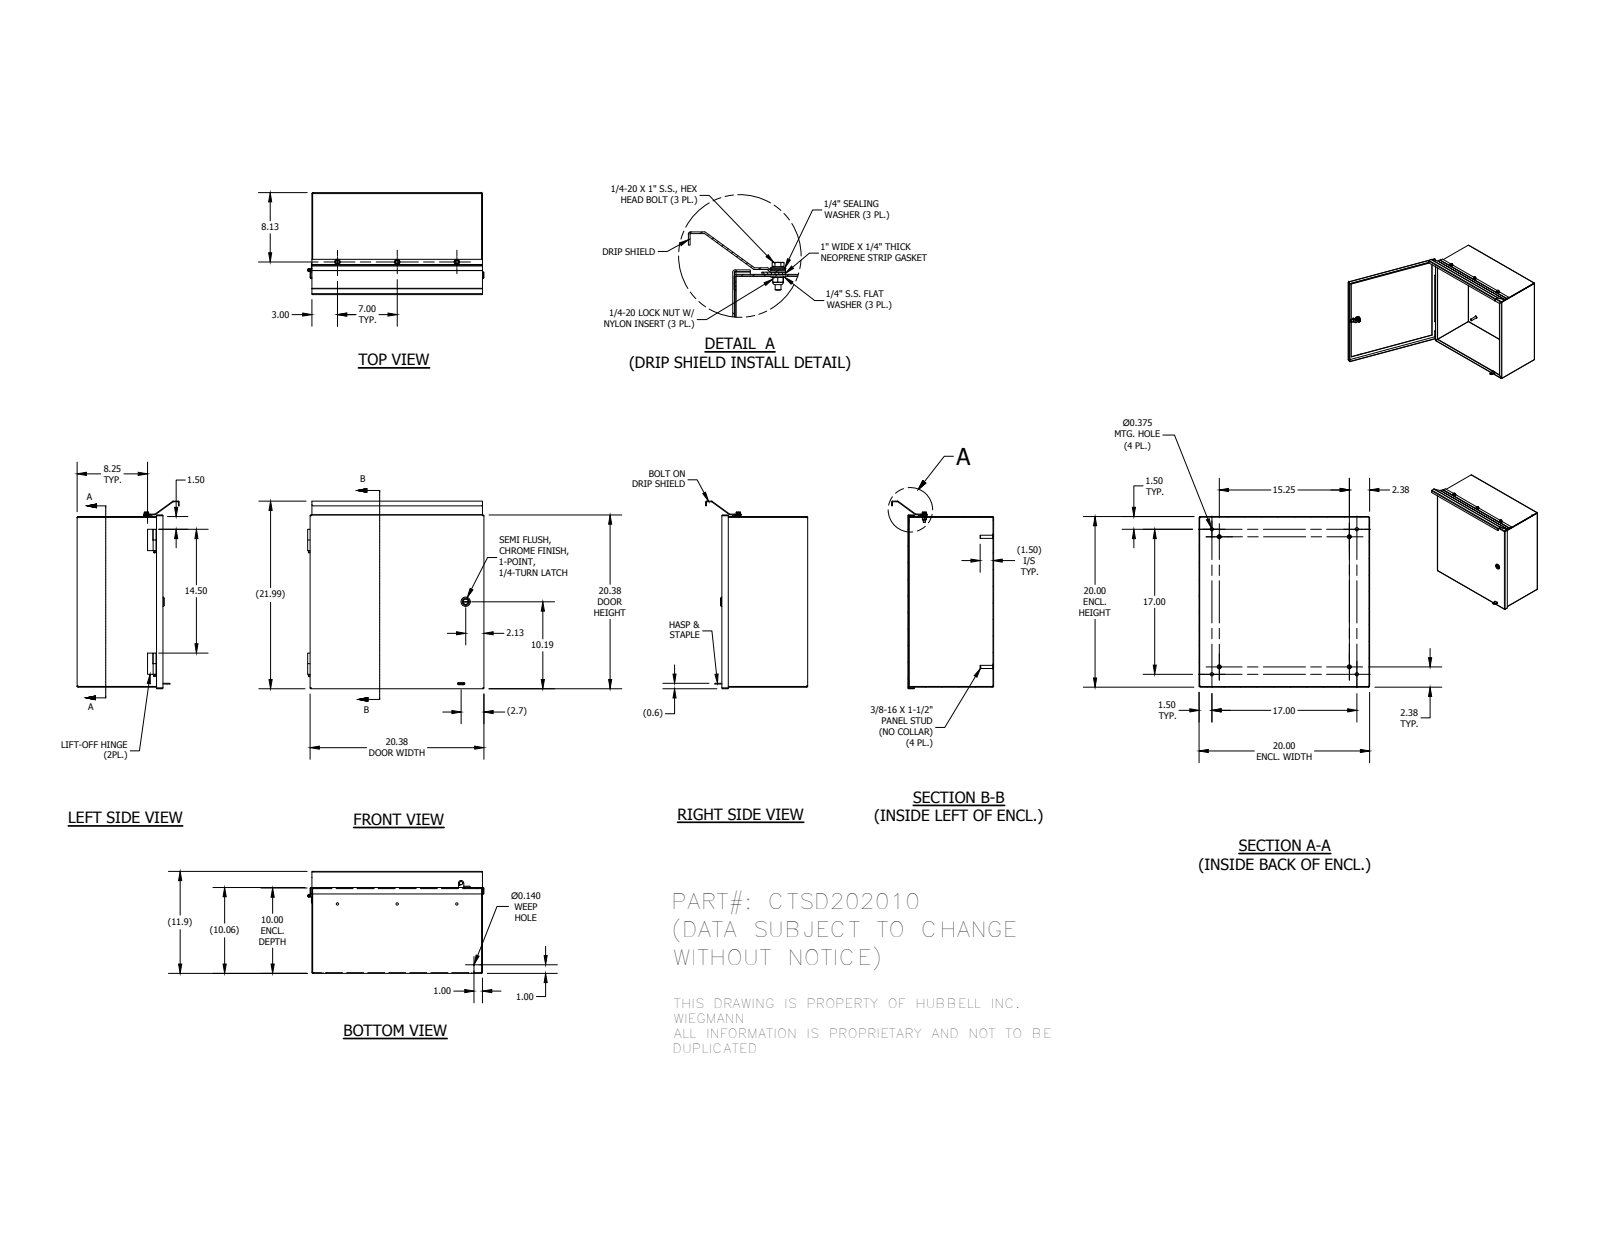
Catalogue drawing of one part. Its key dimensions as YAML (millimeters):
part_name: "CTSD202010BKP; CTSD2020DR; 31815; HC2527 (+8 more)"
step_written_by: "Autodesk Inventor 2014 (AUTOMOTIVE_DESIGN)"
units: millimeters
bodies: {solids: 36, faces: 860, planar: 456, cylindrical: 259, other: 145}
overall_size: [558.67, 524.88, 303.52]
volume: 2305000
surface_area: 2473000
round_holes:
  - {diameter: 9.52, count: 5}
  - {diameter: 4.98, count: 3}
  - {diameter: 5.97, count: 3}
  - {diameter: 6.99, count: 3}
  - {diameter: 7.14, count: 3}
  - {diameter: 7.37, count: 3}
  - {diameter: 3.17, count: 1}
  - {diameter: 3.56, count: 1}
  - {diameter: 5, count: 1}
  - {diameter: 5.36, count: 1}
  - {diameter: 5.56, count: 1}
  - {diameter: 8, count: 1}
round_bosses_or_shafts:
  - {diameter: 11.73, count: 4}
  - {diameter: 9.52, count: 4}
  - {diameter: 16.51, count: 3}
  - {diameter: 15.88, count: 3}
  - {diameter: 15.24, count: 3}
  - {diameter: 11.13, count: 3}
  - {diameter: 11.05, count: 3}
  - {diameter: 6.6, count: 3}
partial_cylinders:
  - {radius: 0.3, count: 30}
  - {radius: 0.79, count: 20}
  - {radius: 2.67, count: 18}
  - {radius: 0.5, count: 10}
  - {radius: 1.78, count: 8}
  - {radius: 3.17, count: 4}
  - {radius: 4, count: 4}
  - {radius: 0.4, count: 3}
face_to_face_distances: [1.88, 253.6, 506.12, 508, 251.72, 255.48, 504.24, 252.12, 1.48, 3.47]
hole_center_spacings: [431.8, 177.8, 216.22, 472.33, 610.66, 7.32, 57.12, 63.41]
